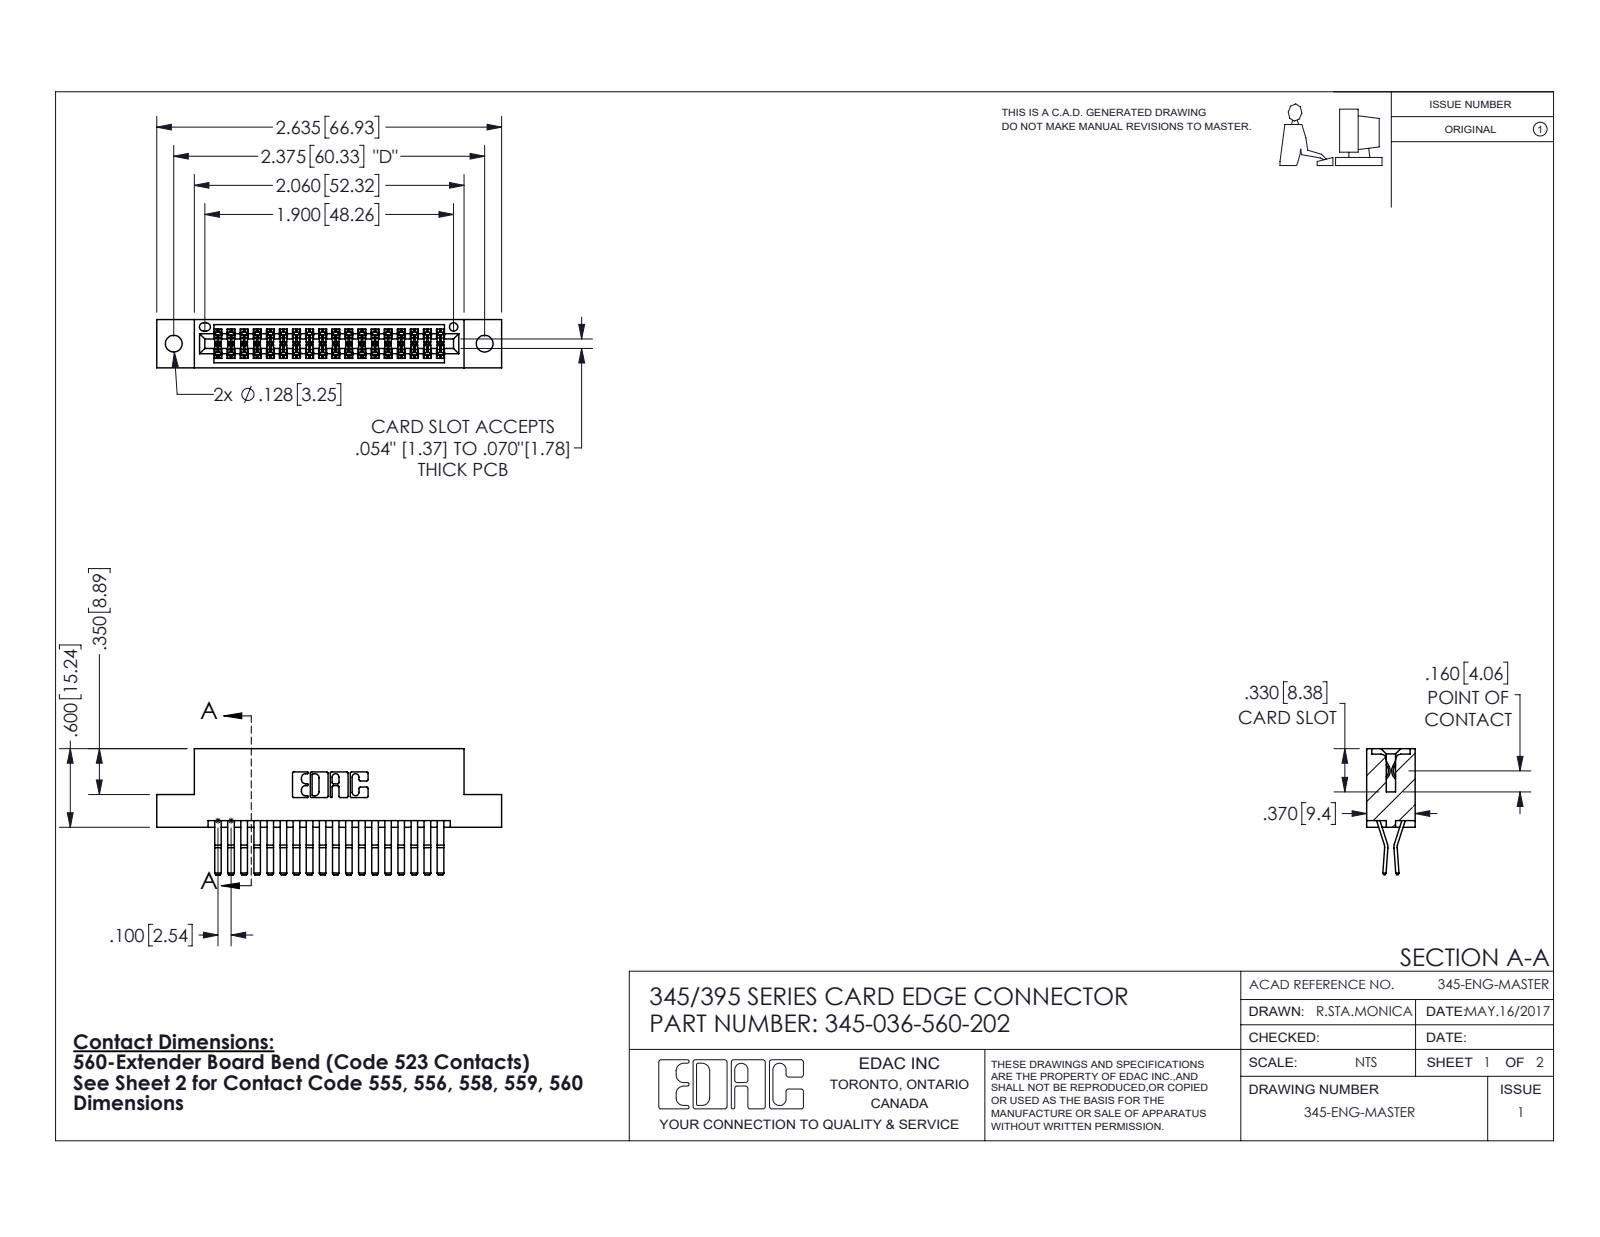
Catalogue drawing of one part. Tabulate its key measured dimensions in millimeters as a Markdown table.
| quantity | value |
| --- | --- |
| part name | 345 Part_Flush Mounting Lugs - 0.128 Dia; 345-292-001_560 Tail; 345-036-560-202 |
| STEP written by | SolidWorks 2016 (CONFIG_CONTROL_DESIGN) |
| units | millimeters |
| bodies | 37 solids, 1998 faces (1268 planar, 730 cylindrical, 0 other) |
| overall size | 66.9 × 24.4 × 9.4 |
| volume | 6 470 mm³ |
| surface area | 9 445 mm² |
| round holes (diameter × count) | 3.3 × 2, 1.6 × 1 |
| partial cylindrical surfaces (radius × count) | 0.2 × 54, 0.3 × 22, 0.2 × 6, 0.8 × 6, 0.7 × 3, 0.3 × 2, 0.4 × 2, 0.5 × 2 |
| main face-to-face distances | 0.6, 7.6, 1.8, 5.1, 9.4, 2.5, 6.9, 5.7, 2.5, 4.4 |
| hole center spacings | 6.9, 54.4, 60.3 |
